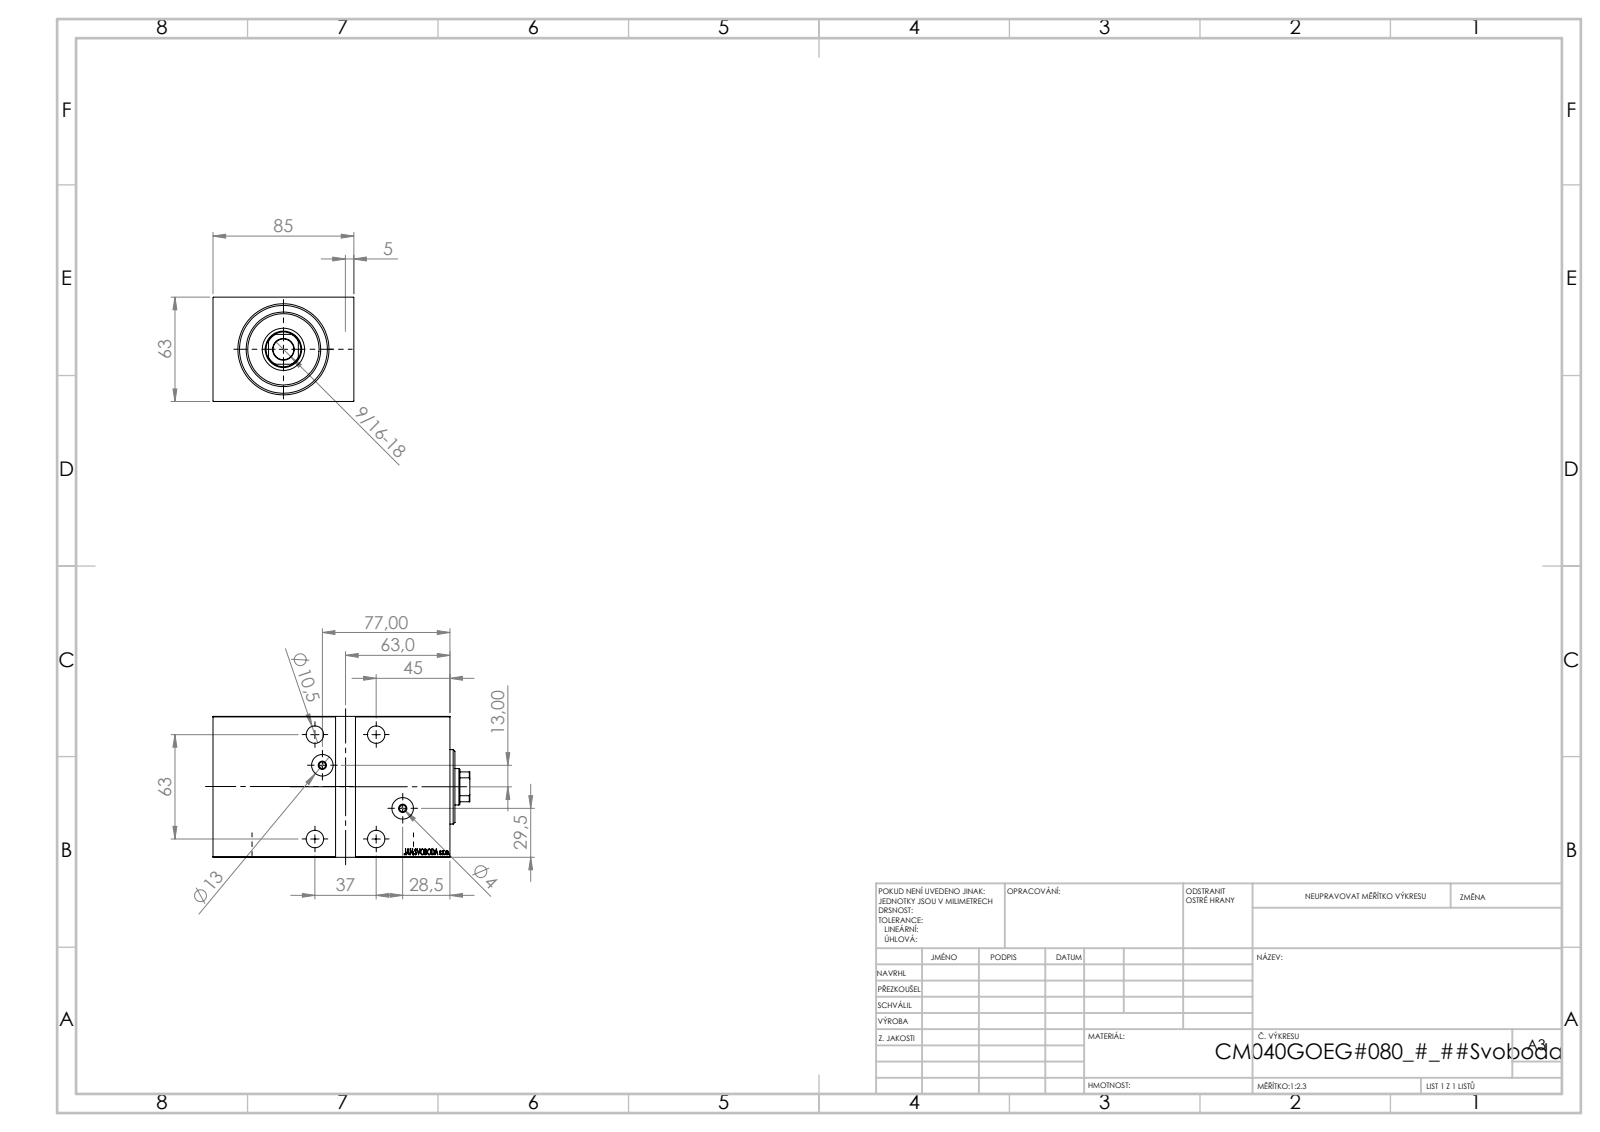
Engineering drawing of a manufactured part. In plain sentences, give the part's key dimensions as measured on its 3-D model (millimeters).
The part is named "Zatka_OIL_PORT; V450CM_VC_G; V450CM_G_VCP; V450CM_G_Body". Its 3-D file was written by "SolidWorks 2019 (CONFIG_CONTROL_DESIGN)". It is 5 solids with 899 faces: 443 planar, 58 cylindrical and 398 other. Overall it measures 155 by 85 by 63 millimeters. Its volume is 663 479 cubic millimeters and its surface area 102 606 square millimeters. Round holes: 4 of diameter 10.5, 4 of diameter 16.5, 2 of diameter 4, 2 of diameter 13, 1 of diameter 12.5, 1 of diameter 22, 1 of diameter 25.5, 1 of diameter 40, 1 of diameter 42, 1 of diameter 53. Round bosses or shafts: 2 of diameter 18, 2 of diameter 5, 1 of diameter 45, 1 of diameter 27. Partial cylindrical surfaces (rounded edges, fillets, slot ends): 1 of radius 10.5. The main face-to-face distances are 63, 85, 143, 12, 131, 5, 138, 126, 3, 60. The hole center spacings are 37, 63, 73.06, 19.04, 24.46, 37.4, 44.73, 47.29.
